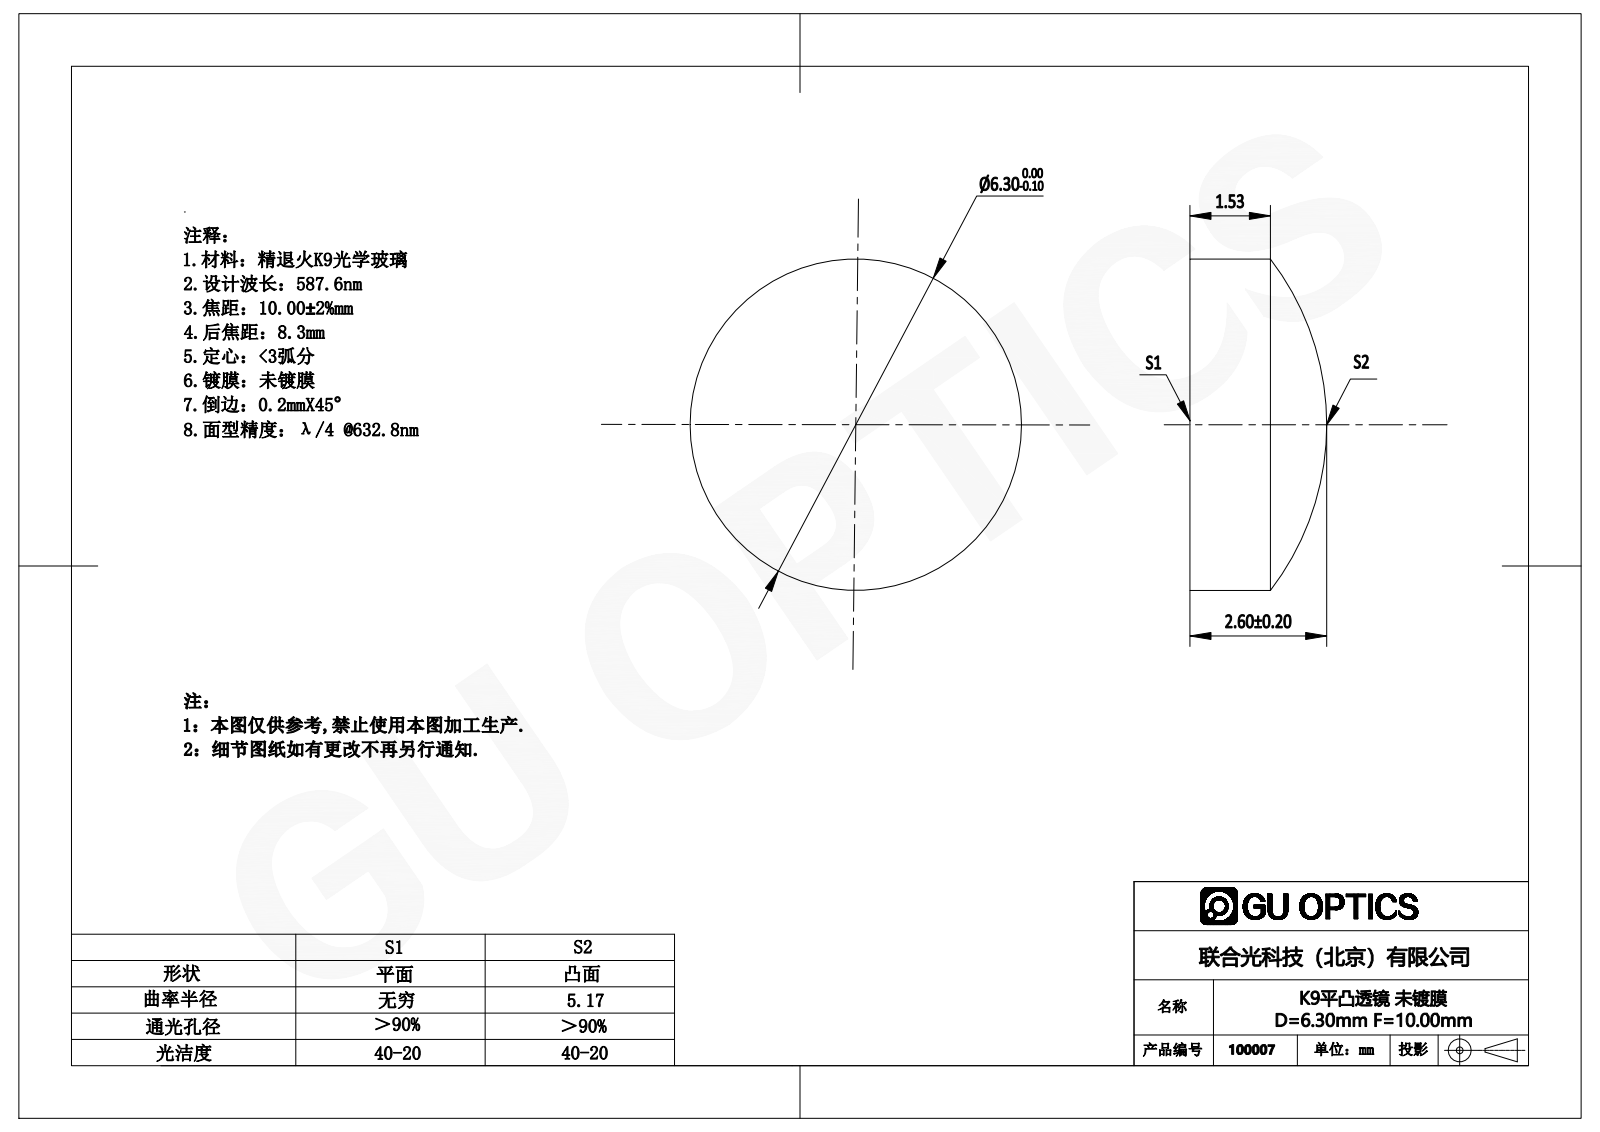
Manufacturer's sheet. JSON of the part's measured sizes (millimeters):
{"part_name": "100007", "step_written_by": "SolidWorks 2016 (AUTOMOTIVE_DESIGN)", "units": "millimeters", "bodies": {"solids": 1, "faces": 5, "planar": 1, "cylindrical": 2, "other": 2}, "overall_size": [6.3, 6.3, 2.6], "volume_mm3": 65, "surface_area_mm2": 96, "round_bosses_or_shafts": [[6.3, 1]]}
